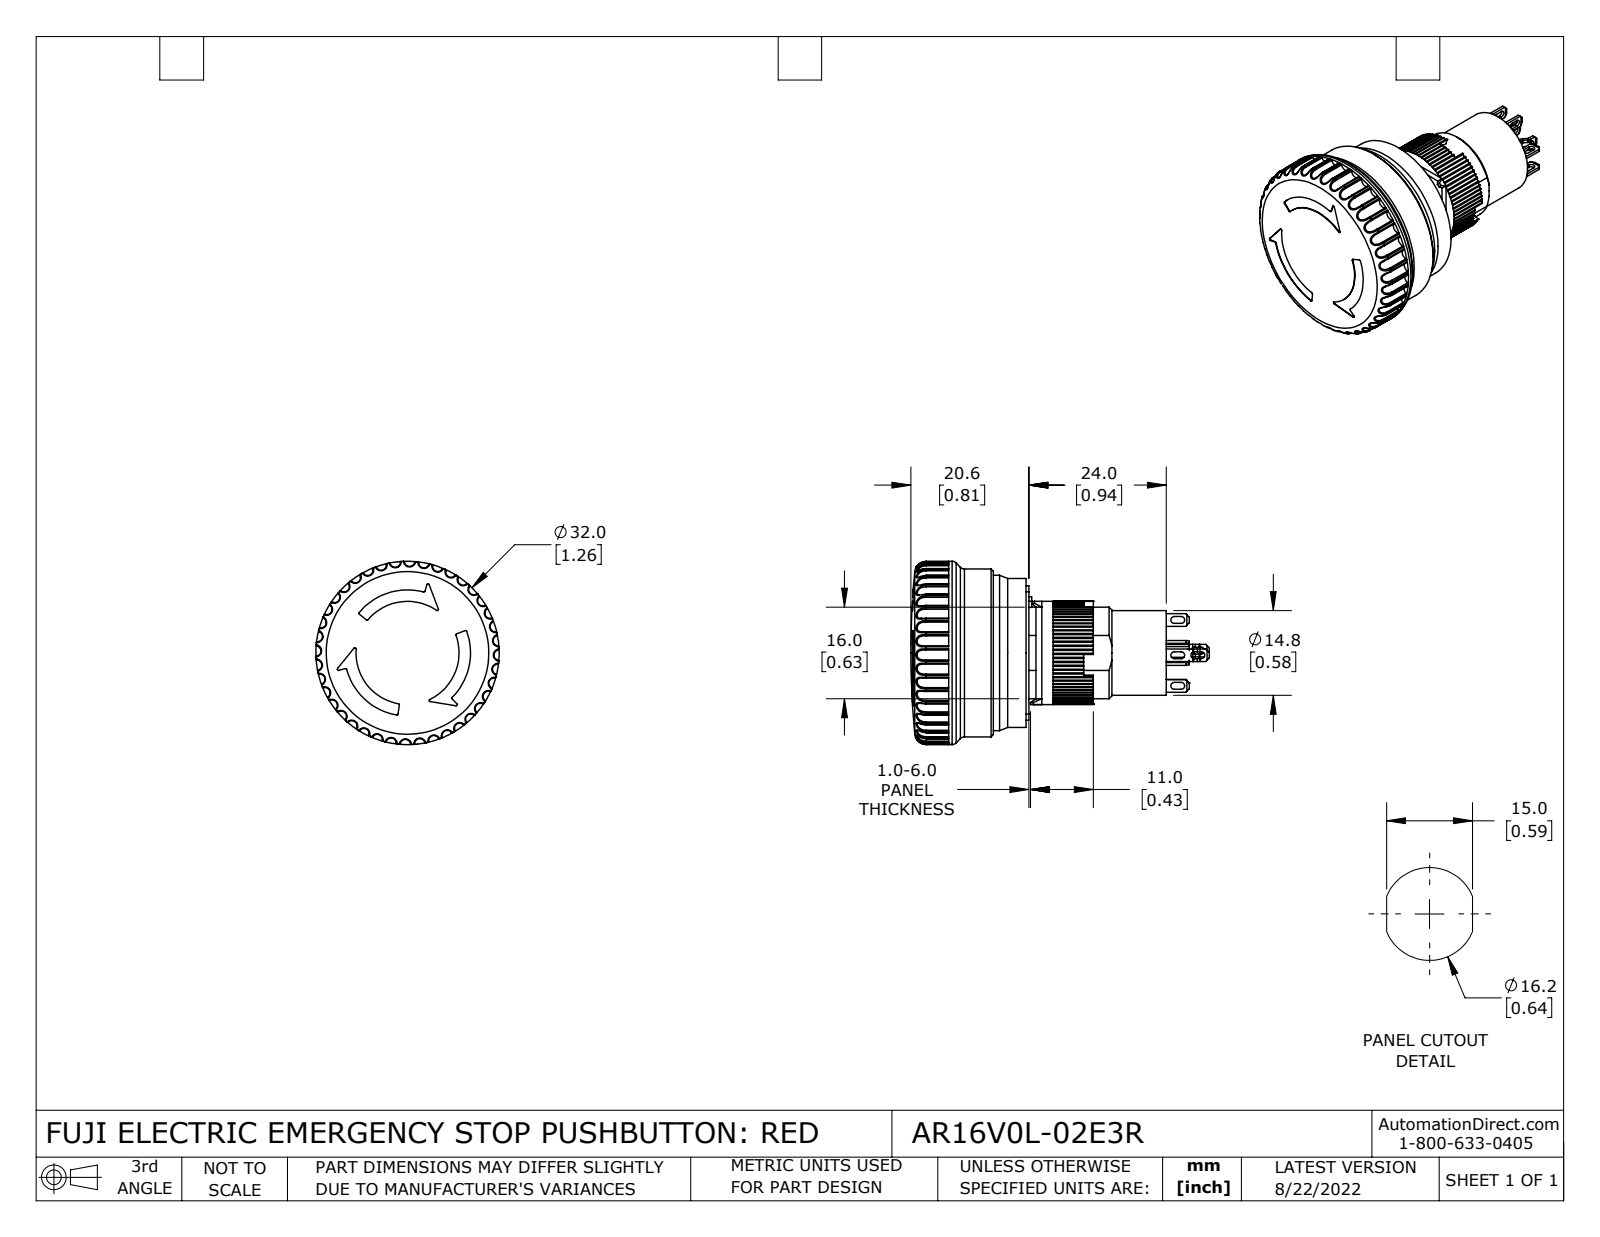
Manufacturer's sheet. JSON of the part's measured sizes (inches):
{"part_name": "AR16V0L-02E3R", "step_written_by": "SolidWorks 2021 (CONFIG_CONTROL_DESIGN)", "units": "inches", "bodies": {"solids": 7, "faces": 1001, "planar": 540, "cylindrical": 387, "other": 74}, "overall_size": [2.051, 1.26, 1.26], "volume_in3": 1.124, "surface_area_in2": 13.68, "round_holes": [[0.583, 1], [0.63, 1], [1.069, 1]], "round_bosses_or_shafts": [[1.26, 1], [1.154, 1], [1.024, 1], [0.858, 1], [0.709, 1], [0.236, 1]], "partial_cylinders_radius": [[0.008, 80], [0.01, 80], [0.035, 40], [0.024, 16], [0.02, 8], [0.01, 4], [0.029, 4], [0.039, 2]], "face_to_face_distances": [0.421, 0.53, 0.108, 0.039, 0.02, 0.069, 0.856, 0.49, 0.089, 0.049]}
